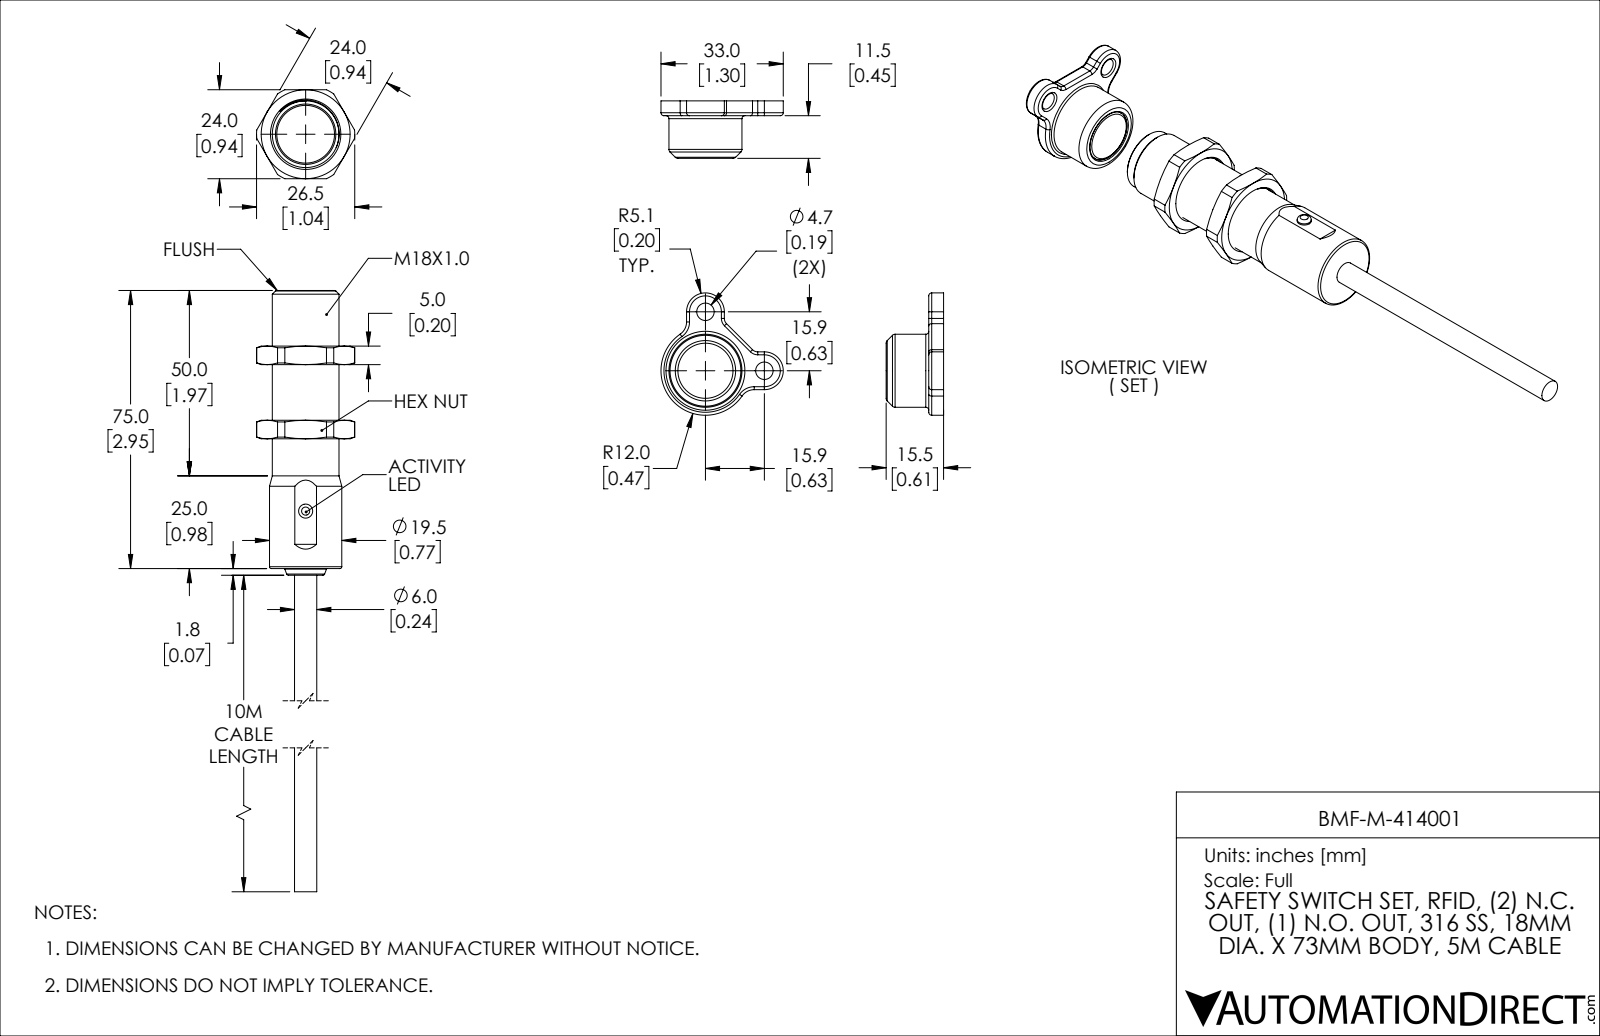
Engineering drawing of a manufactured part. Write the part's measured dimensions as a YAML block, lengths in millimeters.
part_name: "414-BMF"
step_written_by: "SolidWorks 2019 (AUTOMOTIVE_DESIGN)"
units: millimeters
bodies: {solids: 6, faces: 174, planar: 43, cylindrical: 52, other: 79}
overall_size: [183.7, 32.7, 28.3]
volume: 28550
surface_area: 13890
round_holes:
  - {diameter: 4.7, count: 2}
  - {diameter: 2.5, count: 1}
  - {diameter: 12, count: 1}
  - {diameter: 13, count: 1}
  - {diameter: 13.6, count: 1}
  - {diameter: 14.2, count: 1}
  - {diameter: 15.7, count: 1}
  - {diameter: 17.1, count: 1}
  - {diameter: 20.4, count: 1}
round_bosses_or_shafts:
  - {diameter: 20, count: 1}
  - {diameter: 19.5, count: 1}
  - {diameter: 18, count: 1}
  - {diameter: 17.2, count: 1}
  - {diameter: 16.8, count: 1}
  - {diameter: 16.7, count: 1}
  - {diameter: 15, count: 1}
  - {diameter: 6, count: 1}
partial_cylinders:
  - {radius: 0.5, count: 5}
  - {radius: 0.8, count: 5}
  - {radius: 2, count: 2}
  - {radius: 4, count: 2}
  - {radius: 5.1, count: 2}
  - {radius: 12, count: 1}
  - {radius: 13.3, count: 1}
face_to_face_distances: [15, 20, 35, 2, 24, 40, 55, 5, 105.1, 4]
hole_center_spacings: [15.9, 22.5]
